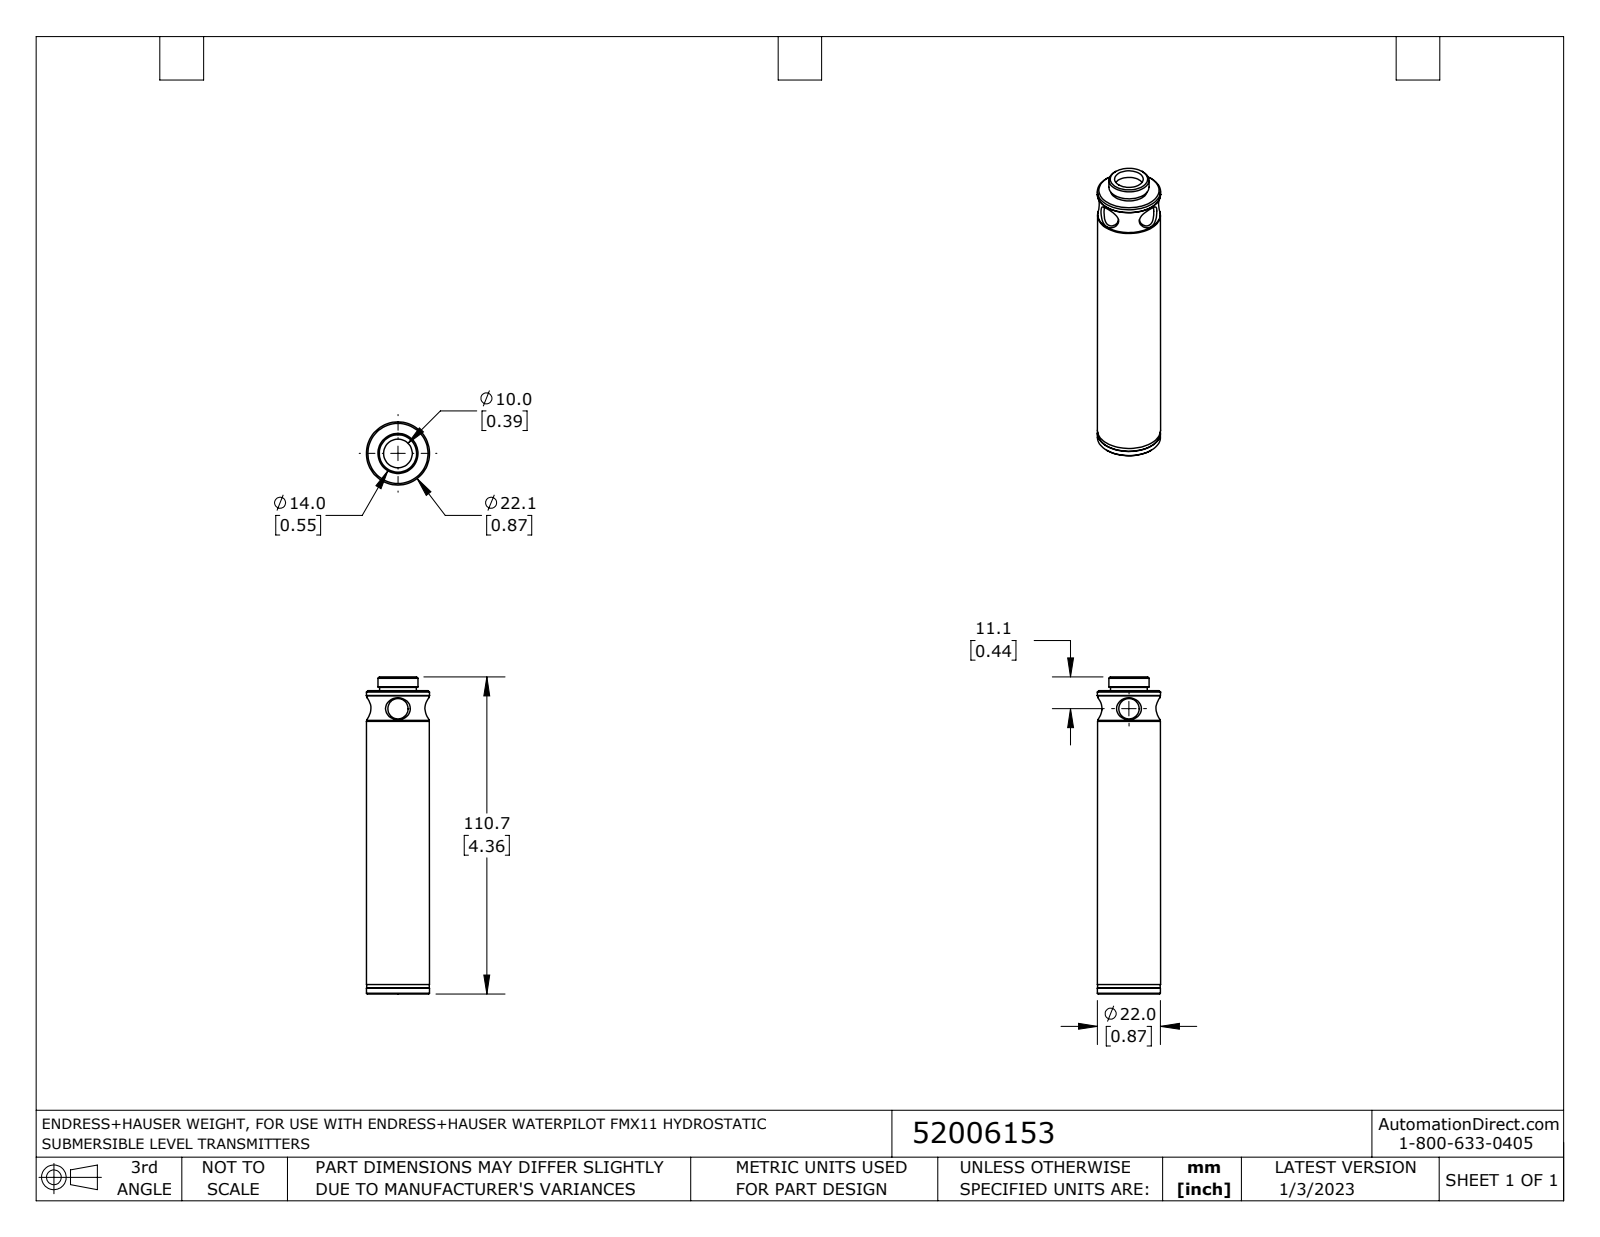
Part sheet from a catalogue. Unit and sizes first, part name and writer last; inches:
Units: inches
Overall size (bounding box): 4.358 × 0.869 × 0.869
Round holes (diameter × count): ⌀0.28 ×2, ⌀0.394 ×1, ⌀0.512 ×1
Round bosses / shafts (diameter × count): ⌀0.867 ×1, ⌀0.86 ×1, ⌀0.551 ×1, ⌀0.506 ×1
Main face-to-face distances: 4.169, 0.232, 3.937, 4.248, 4.016, 0.079, 4.358, 4.126, 0.189, 0.11
Volume: 2.335 in³ · Surface area: 14.14 in²
Bodies: 1 solid, 56 faces (6 planar, 22 cylindrical, 28 other)
Part name (STEP PRODUCT): 52006153 fxt
STEP written by: SolidWorks 2021 (AUTOMOTIVE_DESIGN)
